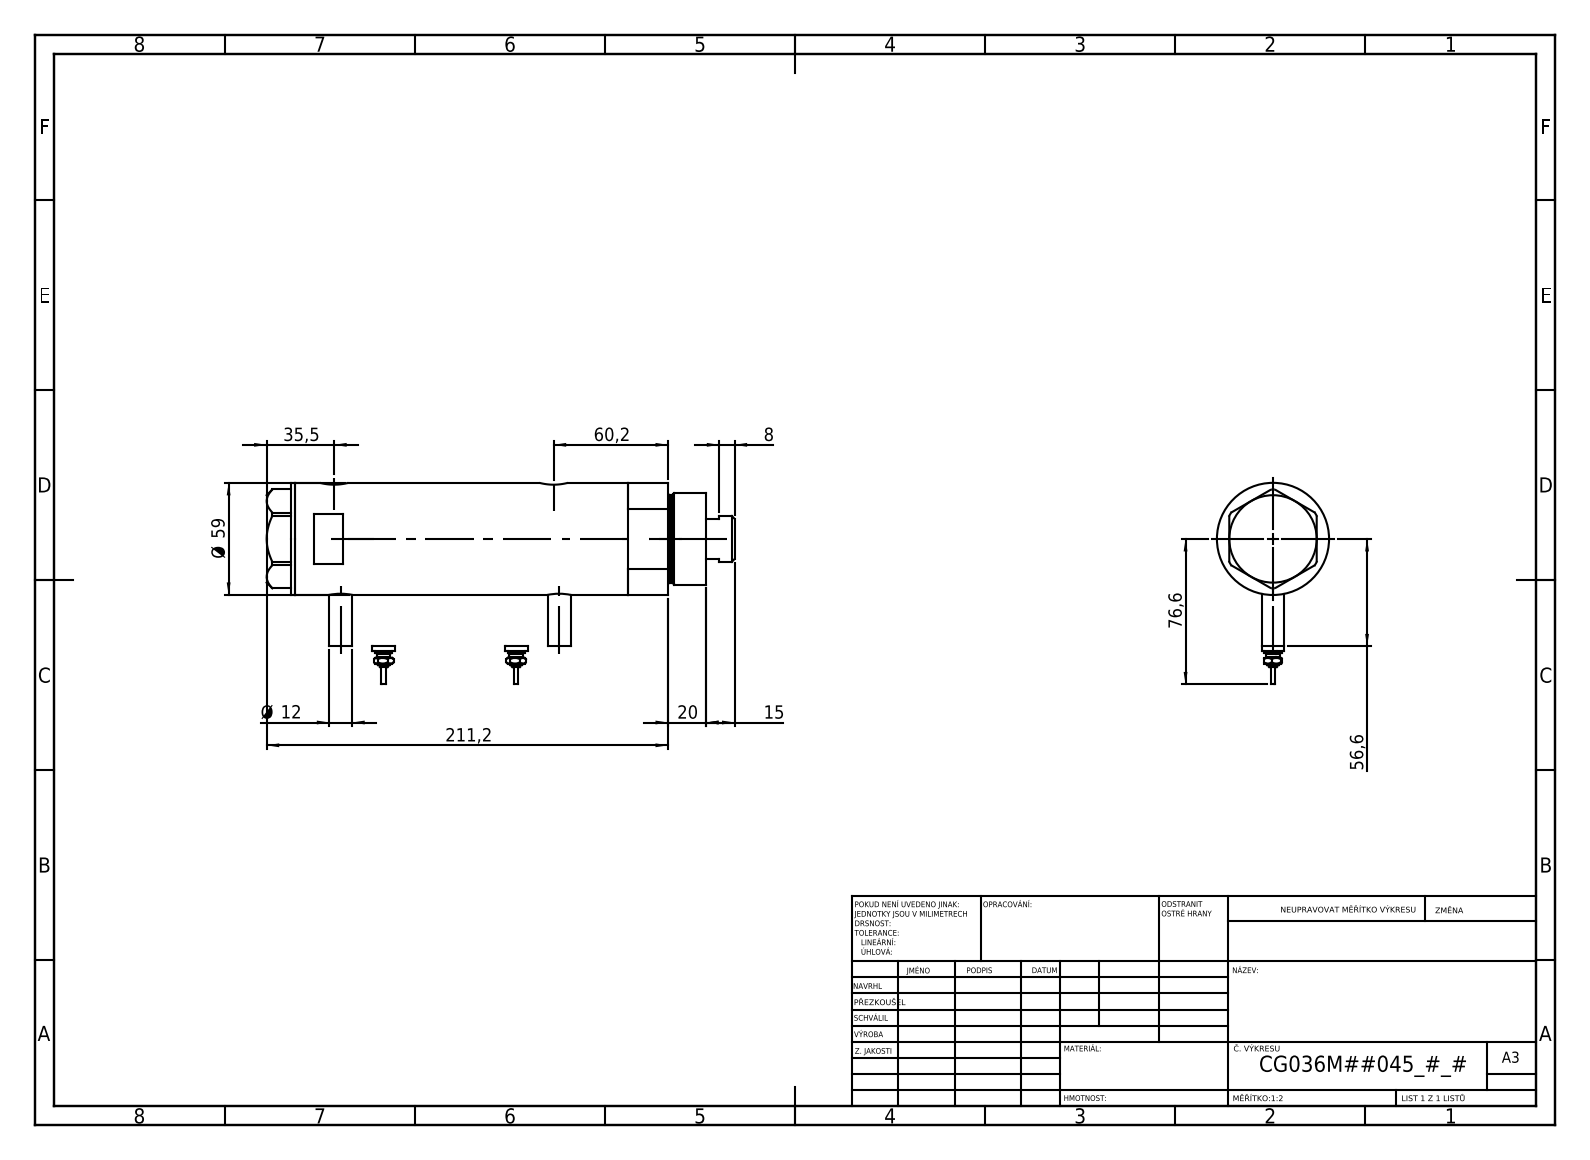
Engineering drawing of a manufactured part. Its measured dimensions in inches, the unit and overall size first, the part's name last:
Units: inches
Overall size (bounding box): 9.693 × 4.177 × 2.323
Round holes (diameter × count): ⌀0.383 ×2, ⌀0.492 ×2, ⌀0.591 ×2, ⌀0.335 ×1, ⌀0.984 ×1, ⌀1.043 ×1, ⌀1.417 ×1, ⌀1.575 ×1, ⌀2.047 ×1
Round bosses / shafts (diameter × count): ⌀0.472 ×4, ⌀0.354 ×2, ⌀0.276 ×2, ⌀0.177 ×2, ⌀0.098 ×2, ⌀2.323 ×1, ⌀1.89 ×1, ⌀1.811 ×1
Main face-to-face distances: 5.402, 0.925, 4.476, 0.591, 1.516, 5.992, 0.079, 9.102, 8.512, 7.587
Hole centre spacings: 0.114, 0.138, 4.409, 4.524, 4.547, 4.661
Volume: 35.56 in³ · Surface area: 181.9 in²
Bodies: 6 solids, 212 faces (79 planar, 69 cylindrical, 64 other)
Part name (STEP PRODUCT): V270CG_FRONT; Switch; V270CG_MIDDLE; V270CG_BACK (+1 more)
STEP written by: SolidWorks 2019 (CONFIG_CONTROL_DESIGN)
